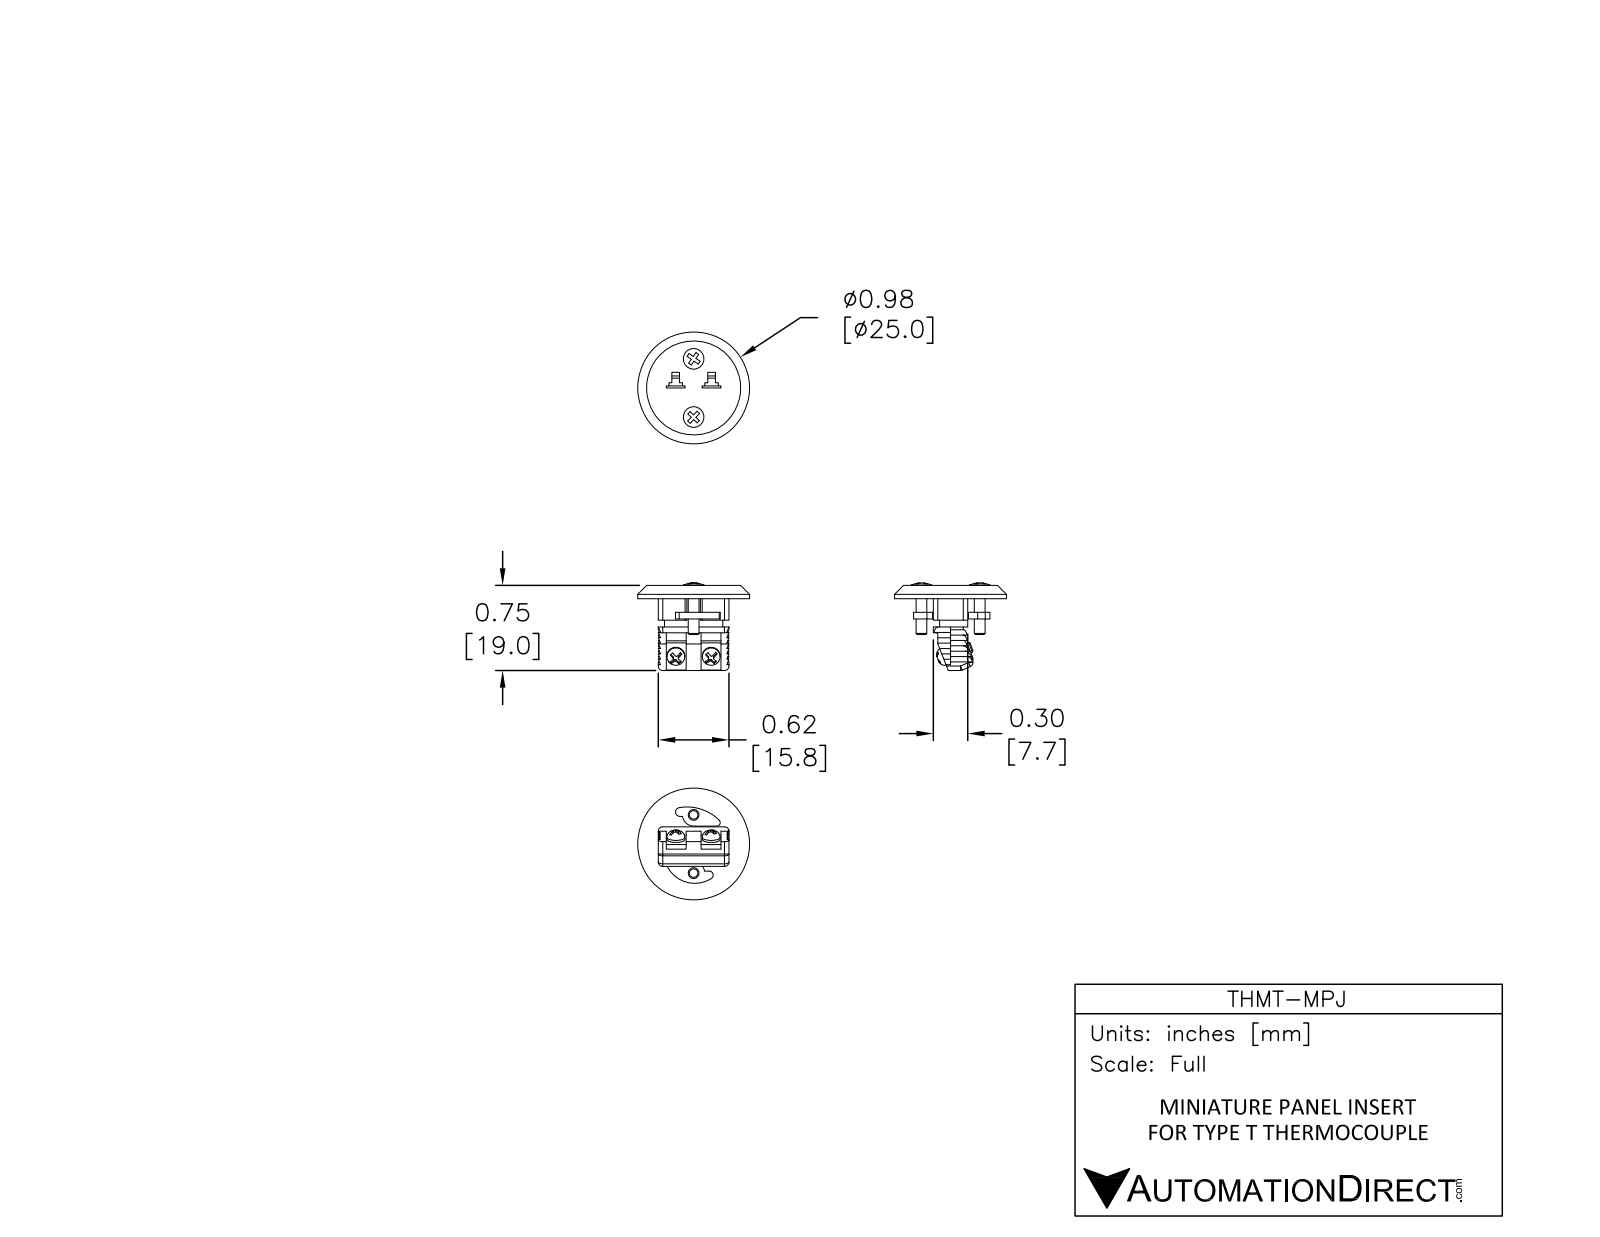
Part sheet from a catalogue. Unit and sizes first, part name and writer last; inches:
Units: inches
Overall size (bounding box): 0.984 × 0.984 × 0.77
Round bosses / shafts (diameter × count): ⌀0.181 ×2, ⌀0.157 ×2, ⌀0.094 ×2, ⌀0.091 ×2, ⌀0.984 ×1
Partial cylindrical surfaces — rounded edges, fillets, slot ends (radius × count): R0.039 ×16, R0.01 ×8, R0.03 ×2, R0.098 ×2, R0.02 ×1, R0.036 ×1, R0.039 ×1, R0.273 ×1
Main face-to-face distances: 0.117, 0.197, 0.059, 0.302, 0.236, 0.07, 0.018, 0.306, 0.027, 0.105
Volume: 0.178 in³ · Surface area: 4.139 in²
Bodies: 1 solid, 357 faces (265 planar, 66 cylindrical, 26 other)
Part name (STEP PRODUCT): THMT-MPJ
STEP written by: SolidWorks 2017 (AUTOMOTIVE_DESIGN)
